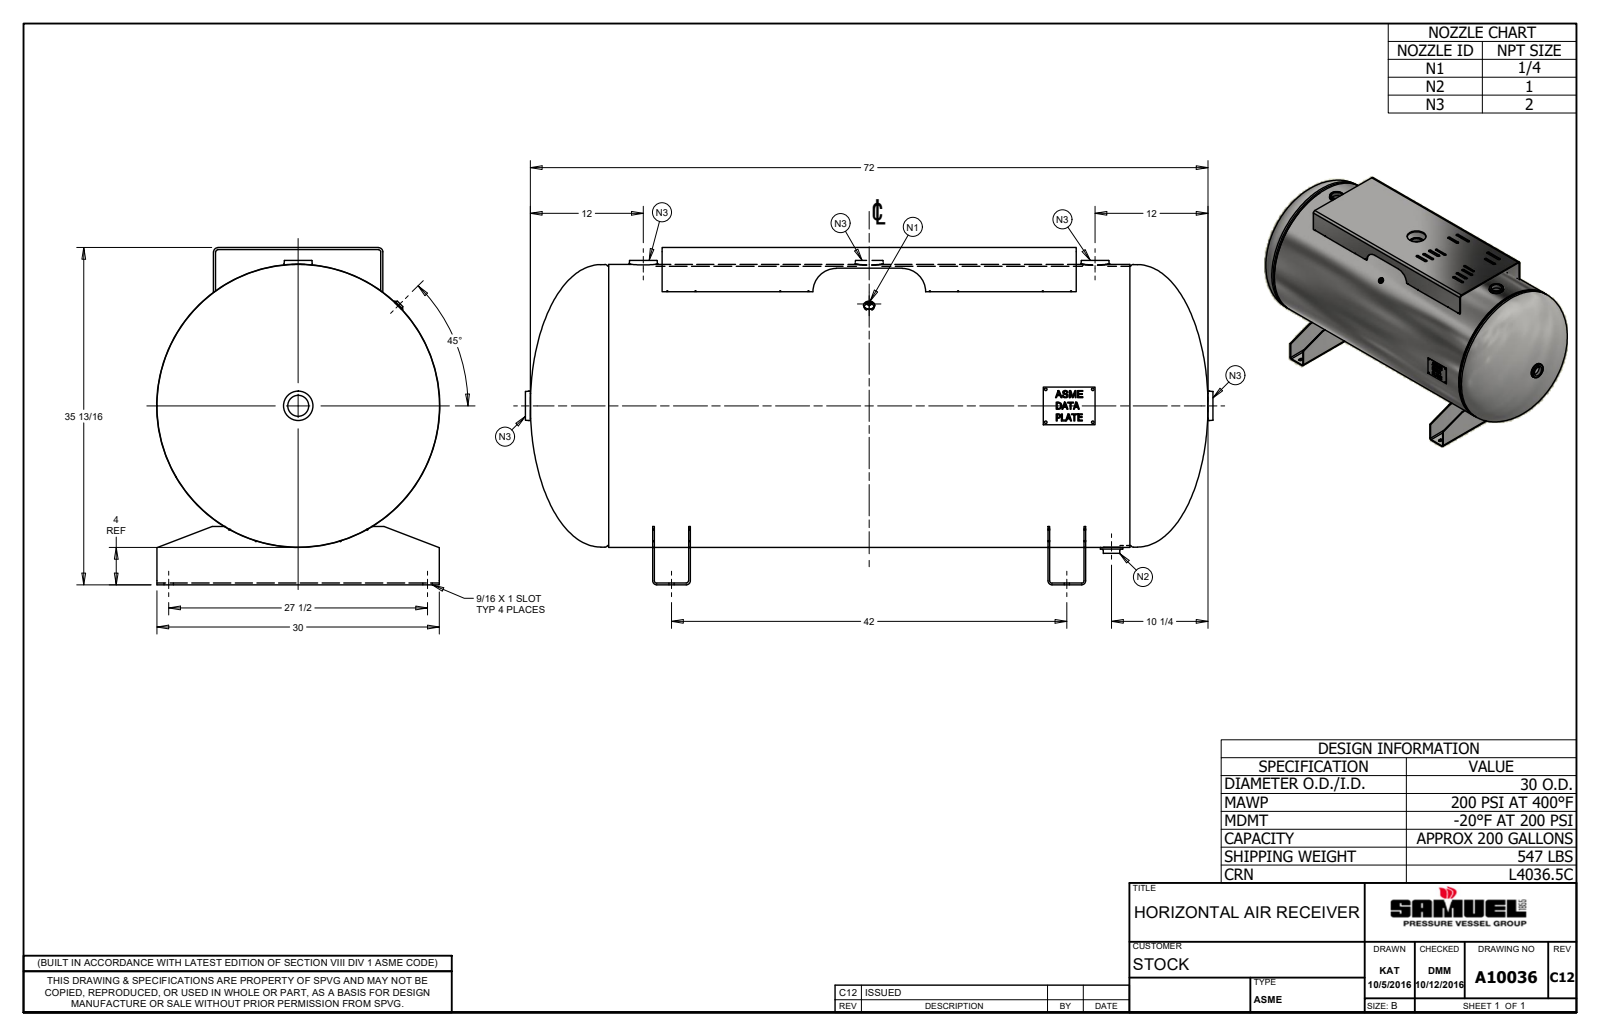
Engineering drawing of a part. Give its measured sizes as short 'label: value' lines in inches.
name: A10036; A10036-1; A10036-2; 910-871-1 (+8 more)
written by: Autodesk Inventor 2019 (CONFIG_CONTROL_DESIGN)
unit: in
bodies: 14 solids, 555 faces (357 planar, 111 cylindrical, 87 other)
size: 73.062 × 35.81 × 30.098
volume: 1 826 in³; area: 18 861 in²
holes: 4× ⌀0.25, 4× ⌀2.231, 4× ⌀2.687, 1× ⌀0.451, 1× ⌀1.063, 1× ⌀1.193, 1× ⌀1.813, 1× ⌀4, 1× ⌀29.294, 1× ⌀29.644, 1× ⌀30
bosses: 3× ⌀3, 3× ⌀2.625, 1× ⌀30.05, 1× ⌀29.65, 1× ⌀3.125, 1× ⌀2.375, 1× ⌀1.75, 1× ⌀1.703
rounds: 20× R0.266, 8× R0.281, 4× R0.203, 4× R0.25, 4× R0.429, 2× R0.224, 2× R0.448, 2× R2.5
face distances: 0.224, 0.179, 3.821, 42, 17.776, 4, 42.179, 45.821, 3.642, 41.821
hole spacings: 3.5, 5, 6.103, 24, 1.75, 25.75, 48, 49.75
